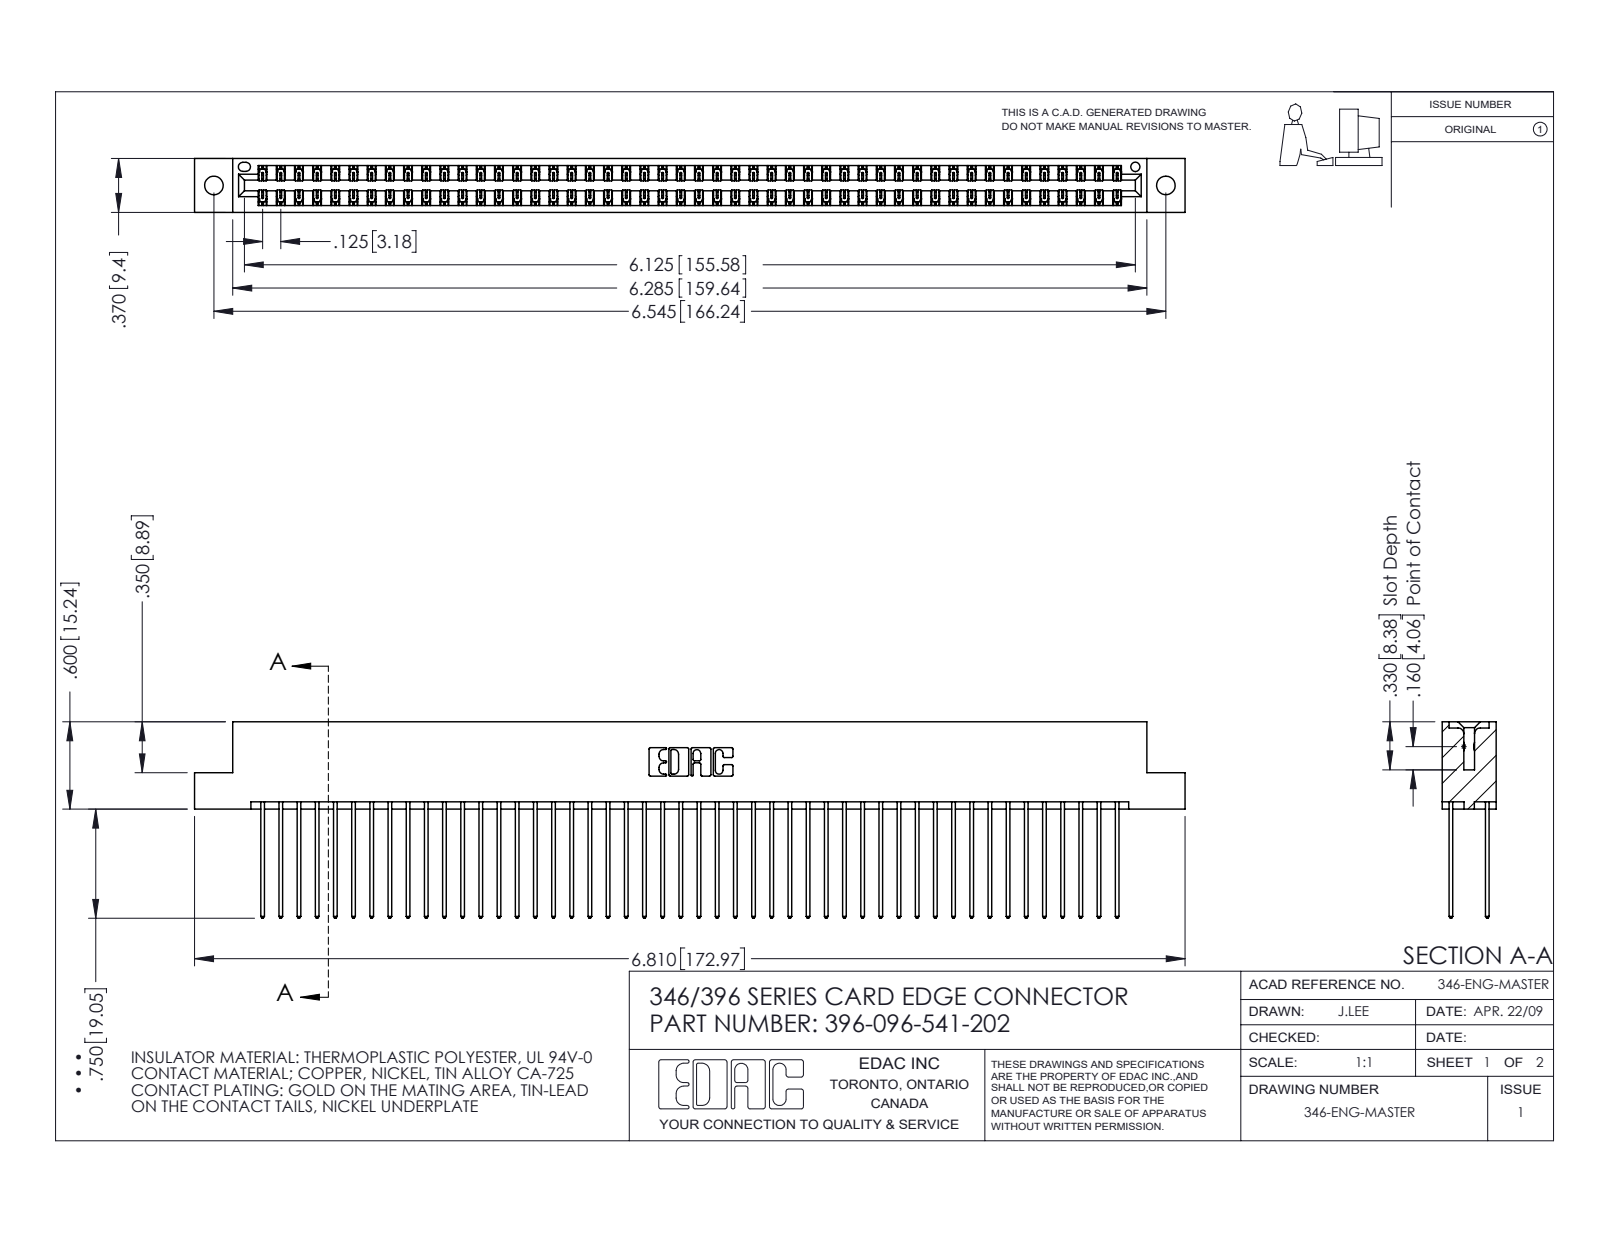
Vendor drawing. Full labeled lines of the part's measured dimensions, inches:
Part name (STEP PRODUCT): 346 Part_Flush Mounting Lugs - 0.128 Dia; 396-096-541-202; 345-292-001_345-293-141
STEP written by: SolidWorks 2016 (CONFIG_CONTROL_DESIGN)
Units: inches
Bodies: 97 solids, 5114 faces (3436 planar, 1678 cylindrical, 0 other)
Overall size (bounding box): 6.81 × 1.35 × 0.37
Volume: 1.064 in³ · Surface area: 40.95 in²
Round holes (diameter × count): ⌀0.128 ×2, ⌀0.064 ×1
Partial cylindrical surfaces — rounded edges, fillets, slot ends (radius × count): R0.006 ×144, R0.01 ×96, R0.01 ×22, R0.007 ×6, R0.031 ×6, R0.026 ×3, R0.014 ×2, R0.022 ×2
Main face-to-face distances: 0.048, 0.322, 0.25, 0.072, 0.298, 0.025, 0.37, 0.275, 0.225, 0.148
Hole centre spacings: 0.246, 6.336, 6.545
